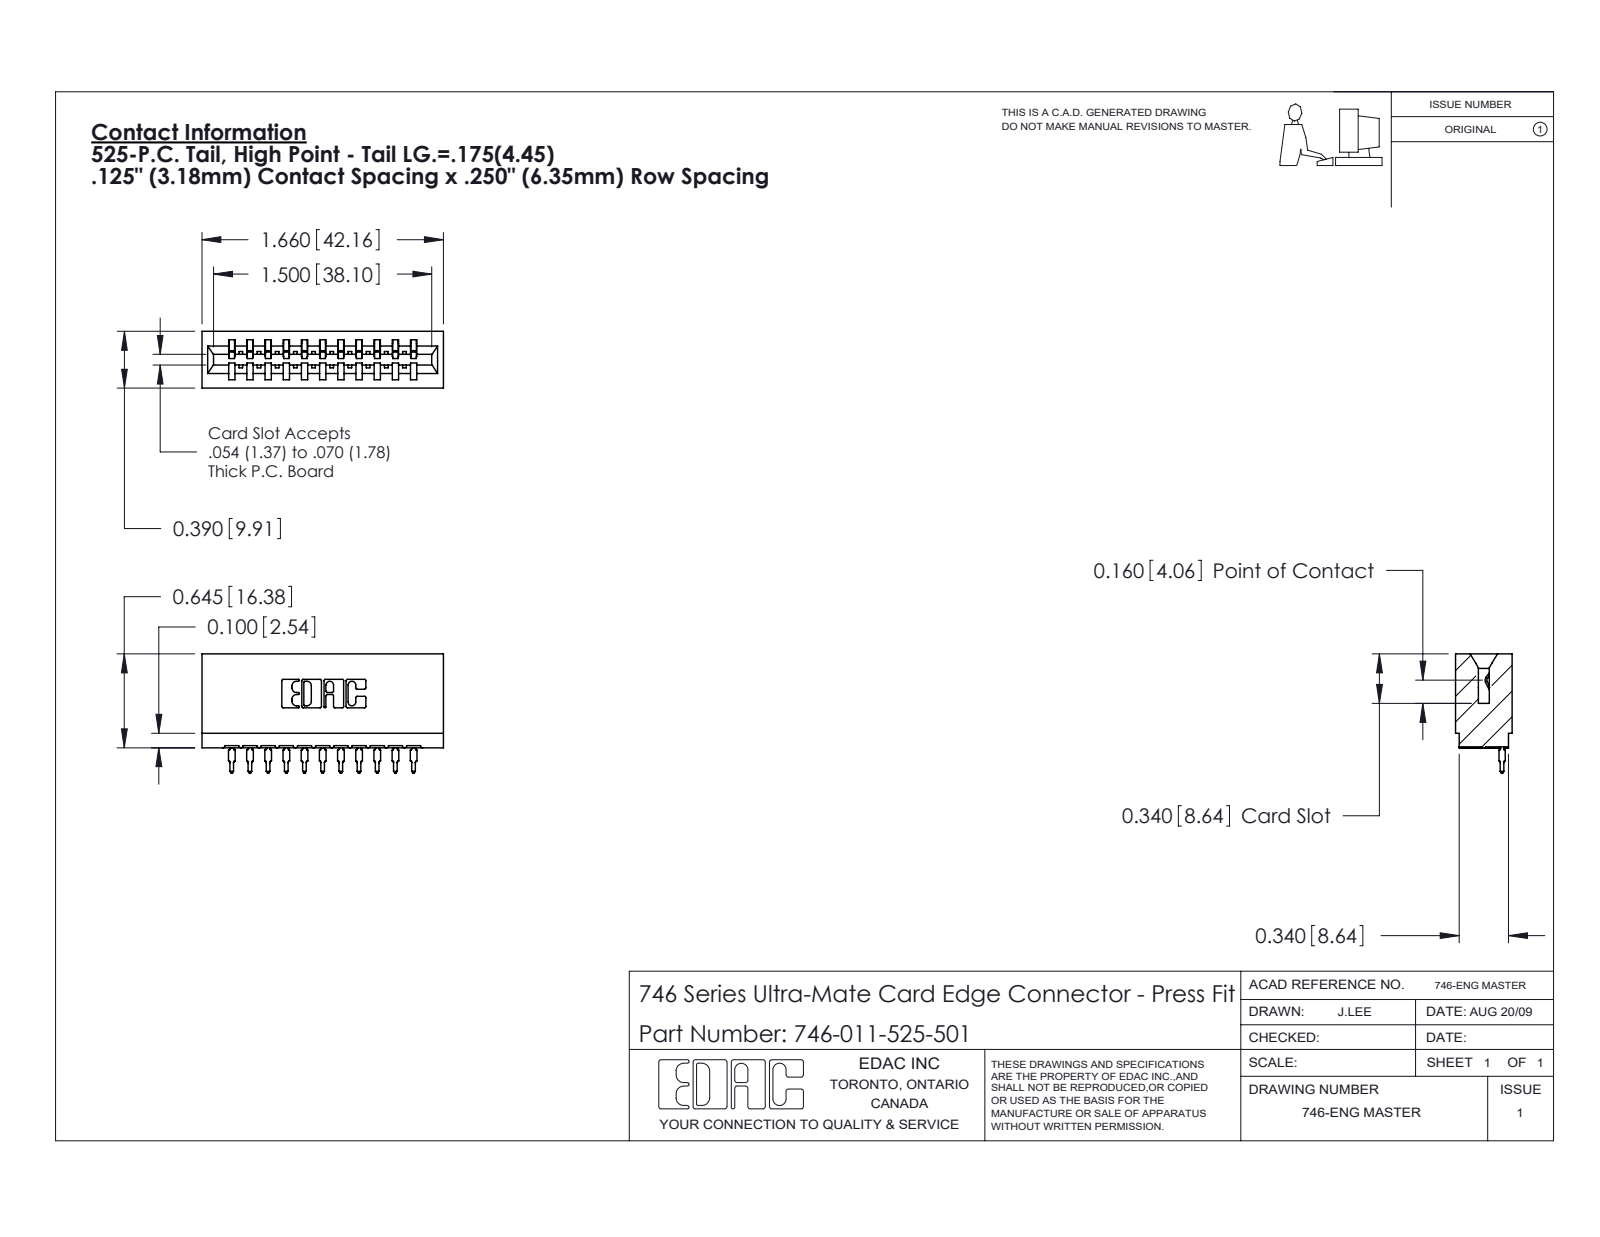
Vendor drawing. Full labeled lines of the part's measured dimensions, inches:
Part name (STEP PRODUCT): 746-011-525-501; 746-292-001_525; 746 Part_.340 Slot Depth - 01
STEP written by: SolidWorks 2020 (CONFIG_CONTROL_DESIGN)
Units: inches
Bodies: 12 solids, 1285 faces (748 planar, 251 cylindrical, 286 other)
Overall size (bounding box): 1.66 × 0.819 × 0.39
Volume: 0.3 in³ · Surface area: 9.441 in²
Partial cylindrical surfaces — rounded edges, fillets, slot ends (radius × count): R0.01 ×22, R0.021 ×22, R0.015 ×12, R0.007 ×6, R0.031 ×6, R0.005 ×4, R0.011 ×4, R0.026 ×3
Main face-to-face distances: 0.25, 0.5, 0.333, 0.125, 0.292, 0.125, 0.057, 0.042, 0.542, 0.39
